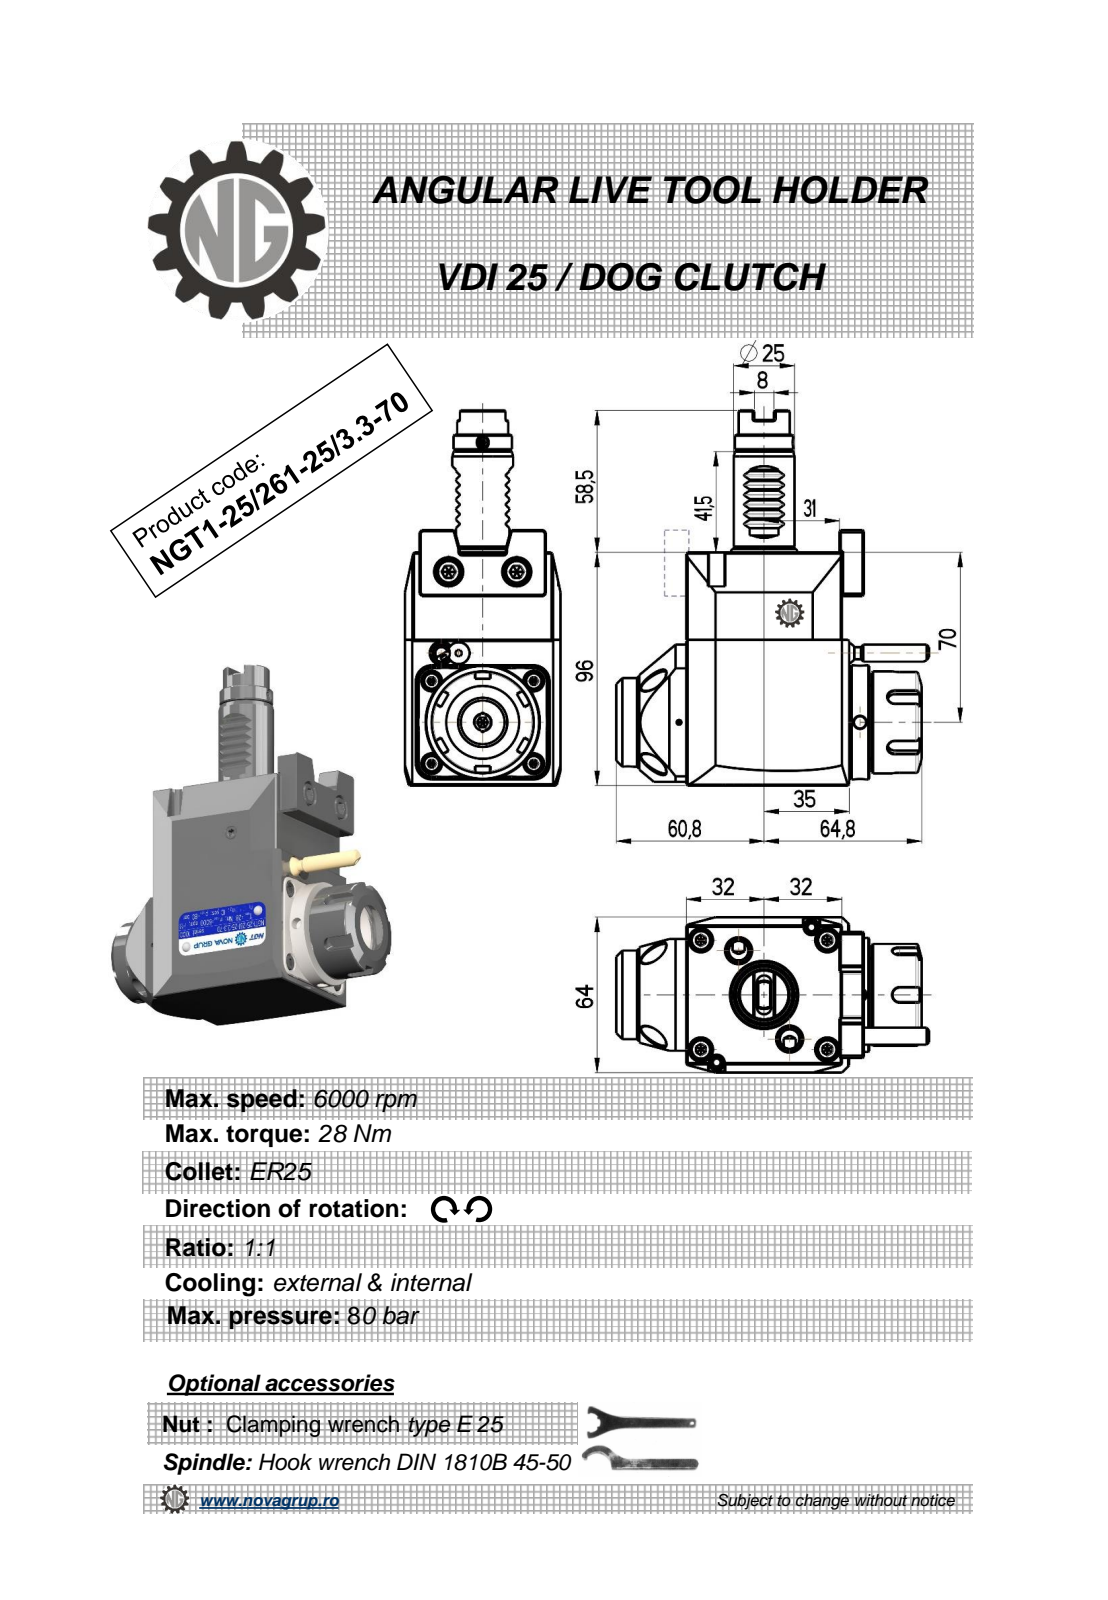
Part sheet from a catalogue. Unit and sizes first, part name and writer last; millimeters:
Units: millimetres
Overall size (bounding box): 154.5 × 128.63 × 64
Round holes (diameter × count): ⌀5 ×2, ⌀2.5 ×1, ⌀3 ×1, ⌀20.3 ×1
Round bosses / shafts (diameter × count): ⌀47 ×1, ⌀42 ×1, ⌀36.5 ×1, ⌀35 ×1, ⌀33 ×1, ⌀25 ×1, ⌀24 ×1, ⌀21 ×1
Partial cylindrical surfaces — rounded edges, fillets, slot ends (radius × count): R0.3 ×12, R0.26 ×6, R3 ×5, R0.5 ×2, R1 ×2, R32 ×1
Main face-to-face distances: 64, 96, 9, 6, 3, 67.2, 3.2, 73, 5.8, 8
Hole centre spacings: 33.19
Volume: 520 287 mm³ · Surface area: 50 923 mm²
Bodies: 1 solid, 422 faces (214 planar, 68 cylindrical, 140 other)
Part name (STEP PRODUCT): NGT1_25_261_25_3_3_70
STEP written by: PRO/ENGINEER BY PARAMETRIC TECHNOLOGY CORPORATION, 2010280 (CONFIG_CONTROL_DESIGN)
